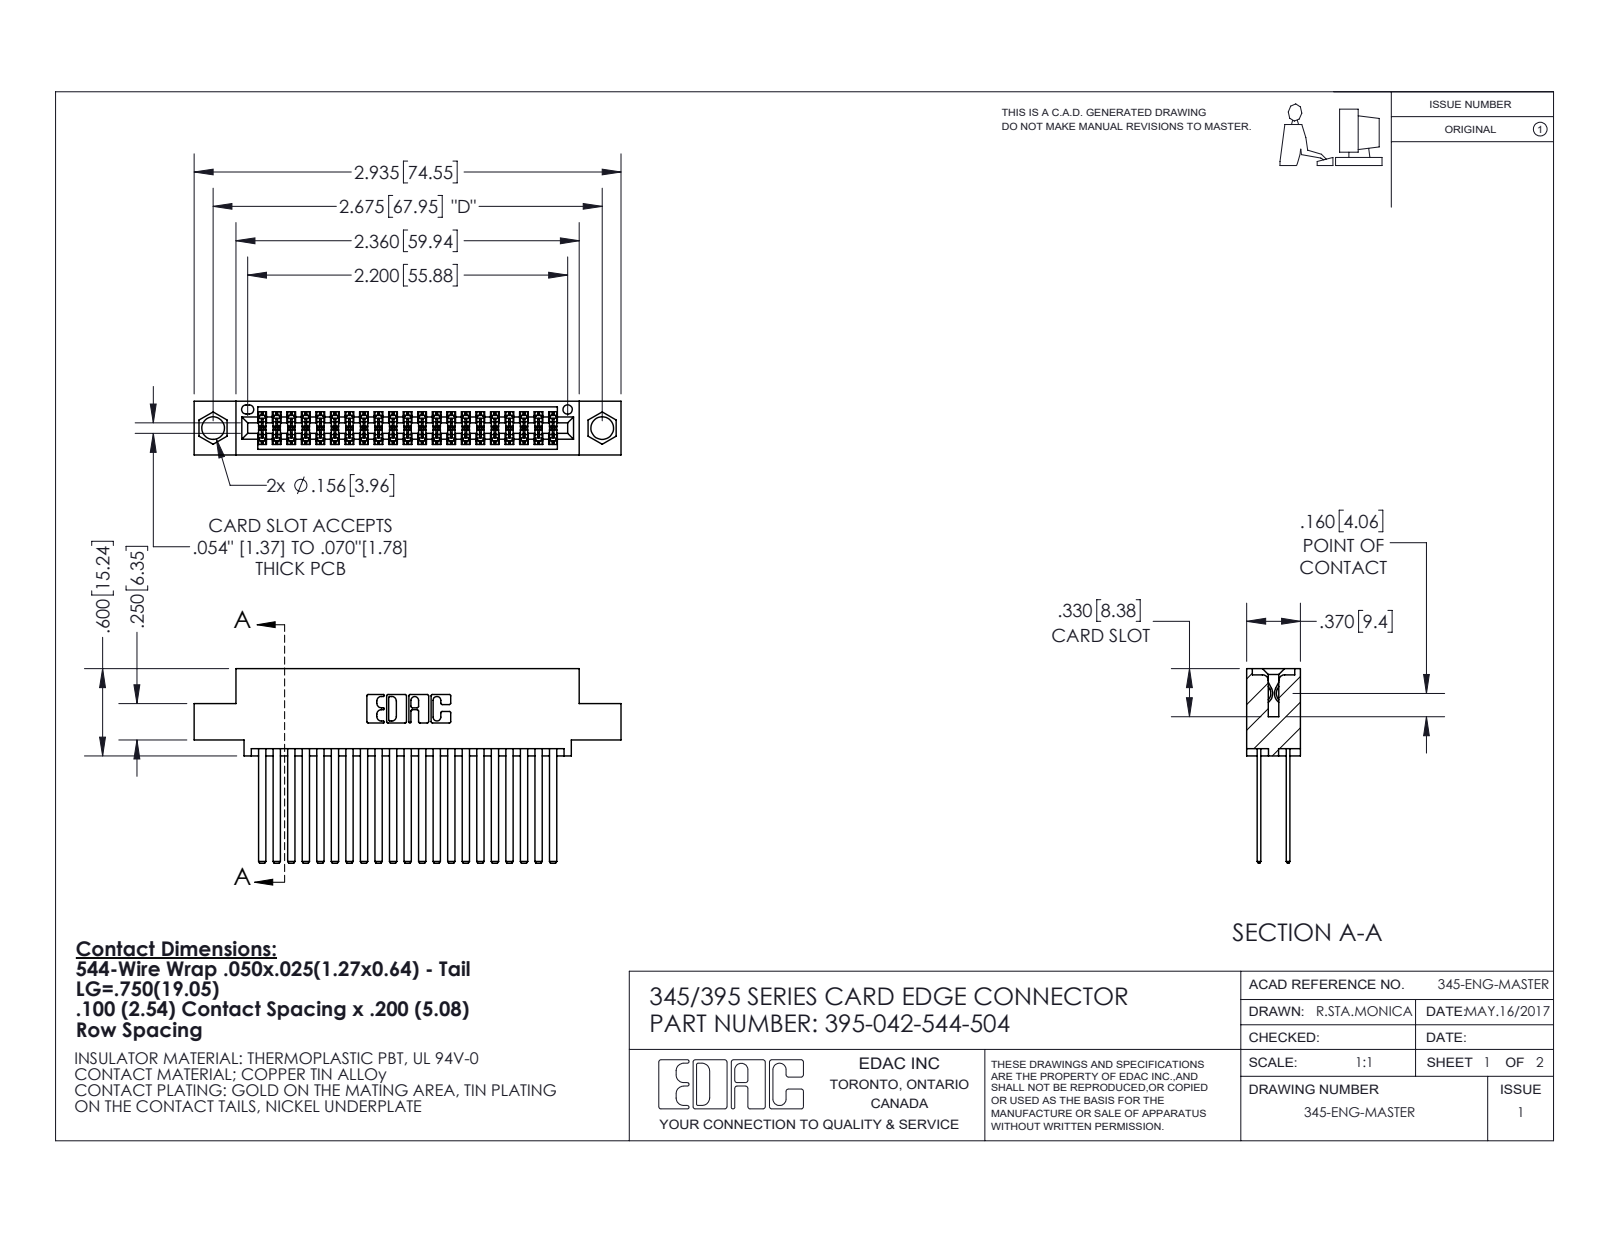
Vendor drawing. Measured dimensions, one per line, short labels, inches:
name: 345 Part_0.110 Offset - 0.156 Dia-TI; 395-042-544-504; 345-292-001_345-293-144
written by: SolidWorks 2020 (CONFIG_CONTROL_DESIGN)
unit: in
bodies: 43 solids, 1992 faces (1316 planar, 676 cylindrical, 0 other)
size: 2.935 × 1.337 × 0.37
volume: 0.455 in³; area: 19.04 in²
holes: 2× ⌀0.156, 1× ⌀0.064
rounds: 63× R0.006, 22× R0.01, 6× R0.007, 6× R0.031, 3× R0.026, 2× R0.014, 2× R0.019, 2× R0.022
face distances: 0.2, 0.298, 0.072, 0.098, 0.272, 0.025, 0.225, 0.37, 0.175, 0.05
hole spacings: 0.27, 2.441, 2.675
